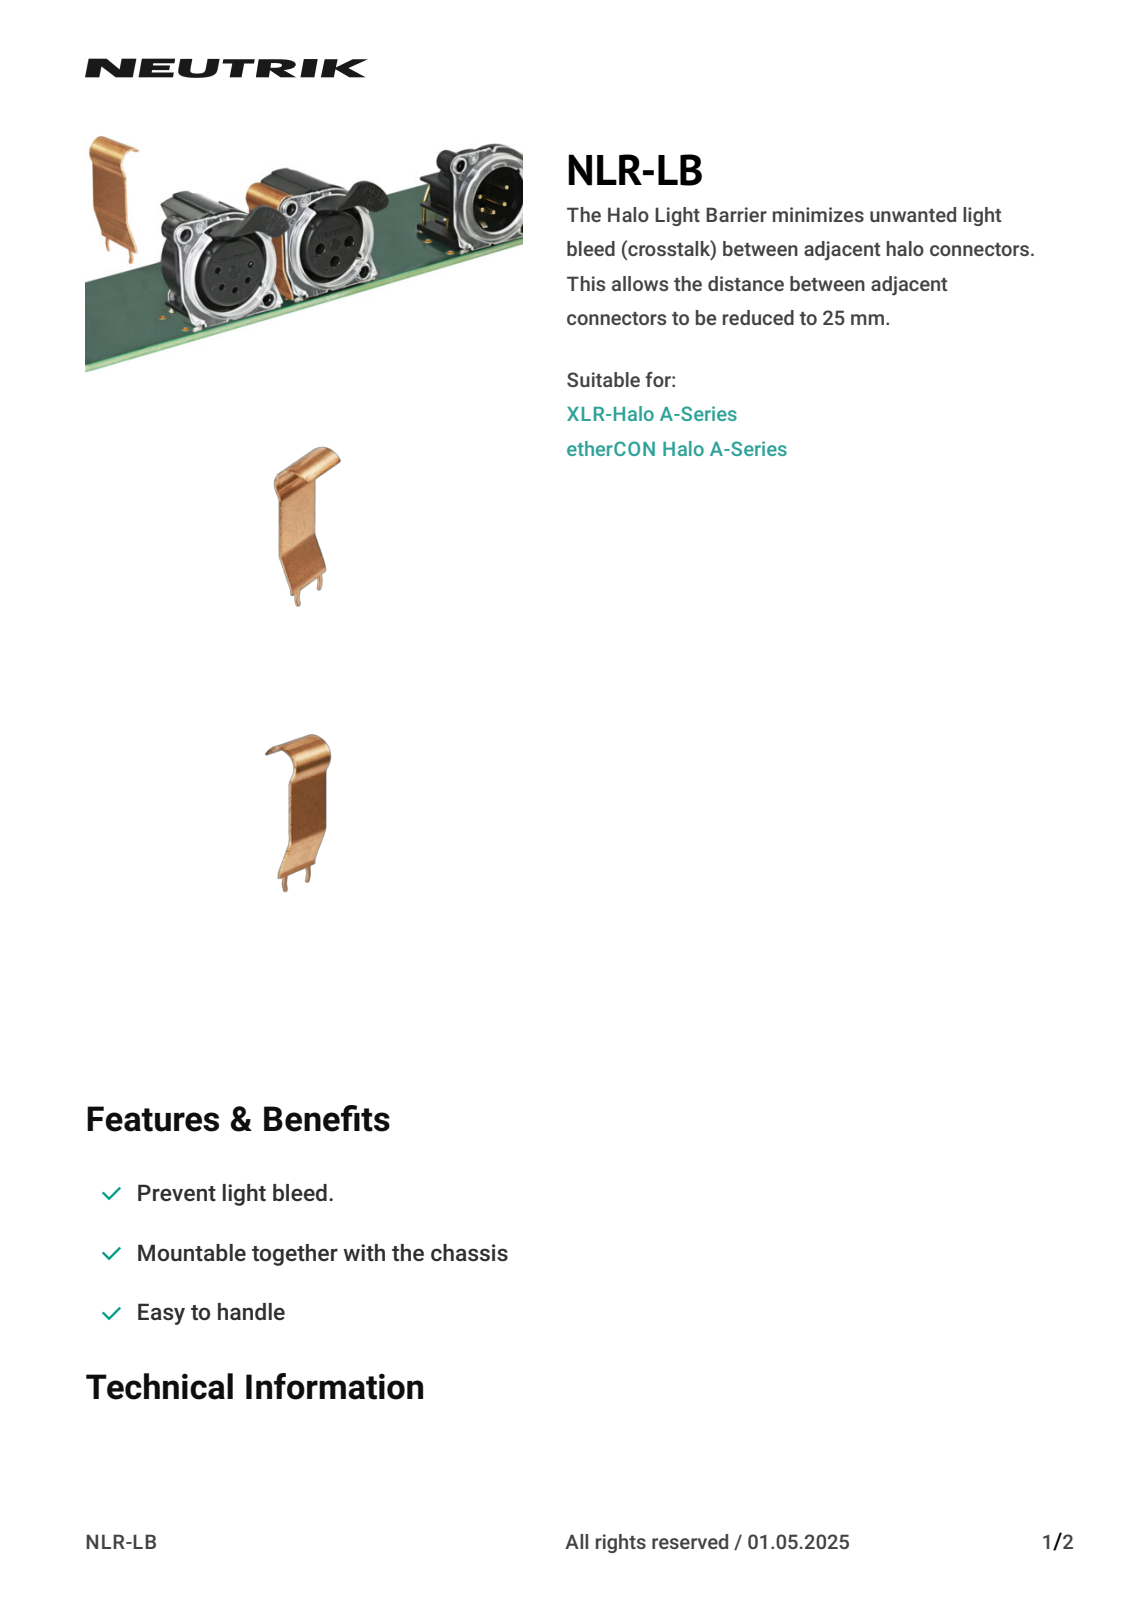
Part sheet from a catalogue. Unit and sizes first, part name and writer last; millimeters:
Units: millimetres
Overall size (bounding box): 29.37 × 12 × 6.88
Partial cylindrical surfaces — rounded edges, fillets, slot ends (radius × count): R0.6 ×3, R1.2 ×3, R0.4 ×2, R1.85 ×1, R2.45 ×1, R2.88 ×1, R3.2 ×1, R3.48 ×1
Main face-to-face distances: 0.59, 0.61, 12, 0.6, 0.8, 24.96, 11, 1
Volume: 231 mm³ · Surface area: 834 mm²
Bodies: 1 solid, 48 faces (24 planar, 16 cylindrical, 8 other)
Part name (STEP PRODUCT): 30010169
STEP written by: CREO PARAMETRIC BY PTC INC, 2021184 (CONFIG_CONTROL_DESIGN)
